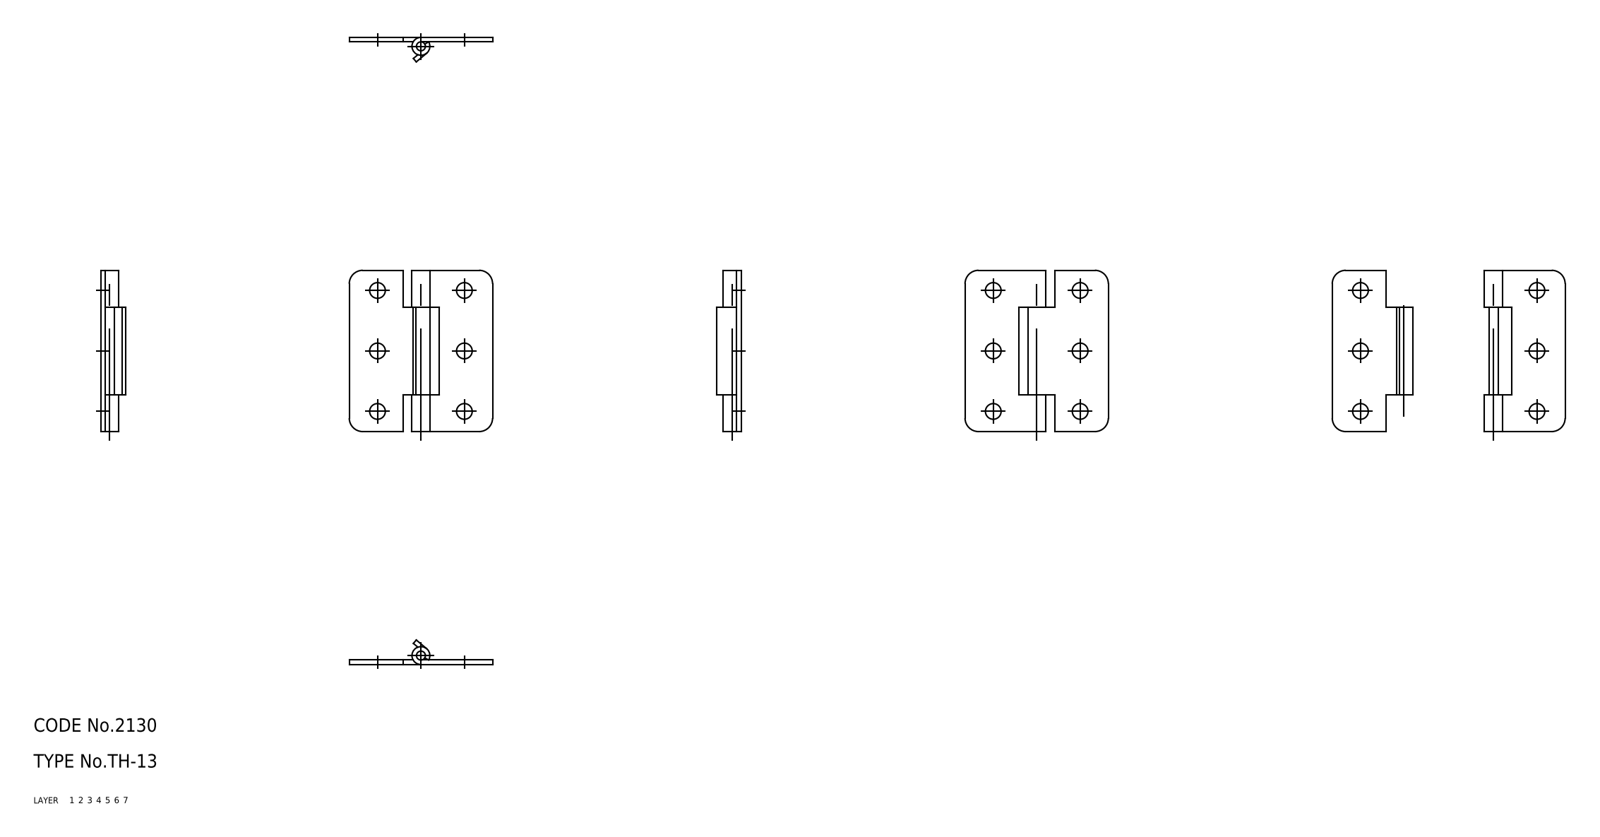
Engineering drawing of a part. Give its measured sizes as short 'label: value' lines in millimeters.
name: shaft; hinge piece_B; hinge piece_A; TH_13_3370_36
written by: CADfix (AUTOMOTIVE_DESIGN)
unit: mm
bodies: 3 solids, 48 faces (0 planar, 0 cylindrical, 48 other)
size: 36 × 32 × 5.48
volume: 1 315 mm³; area: 2 958 mm²
